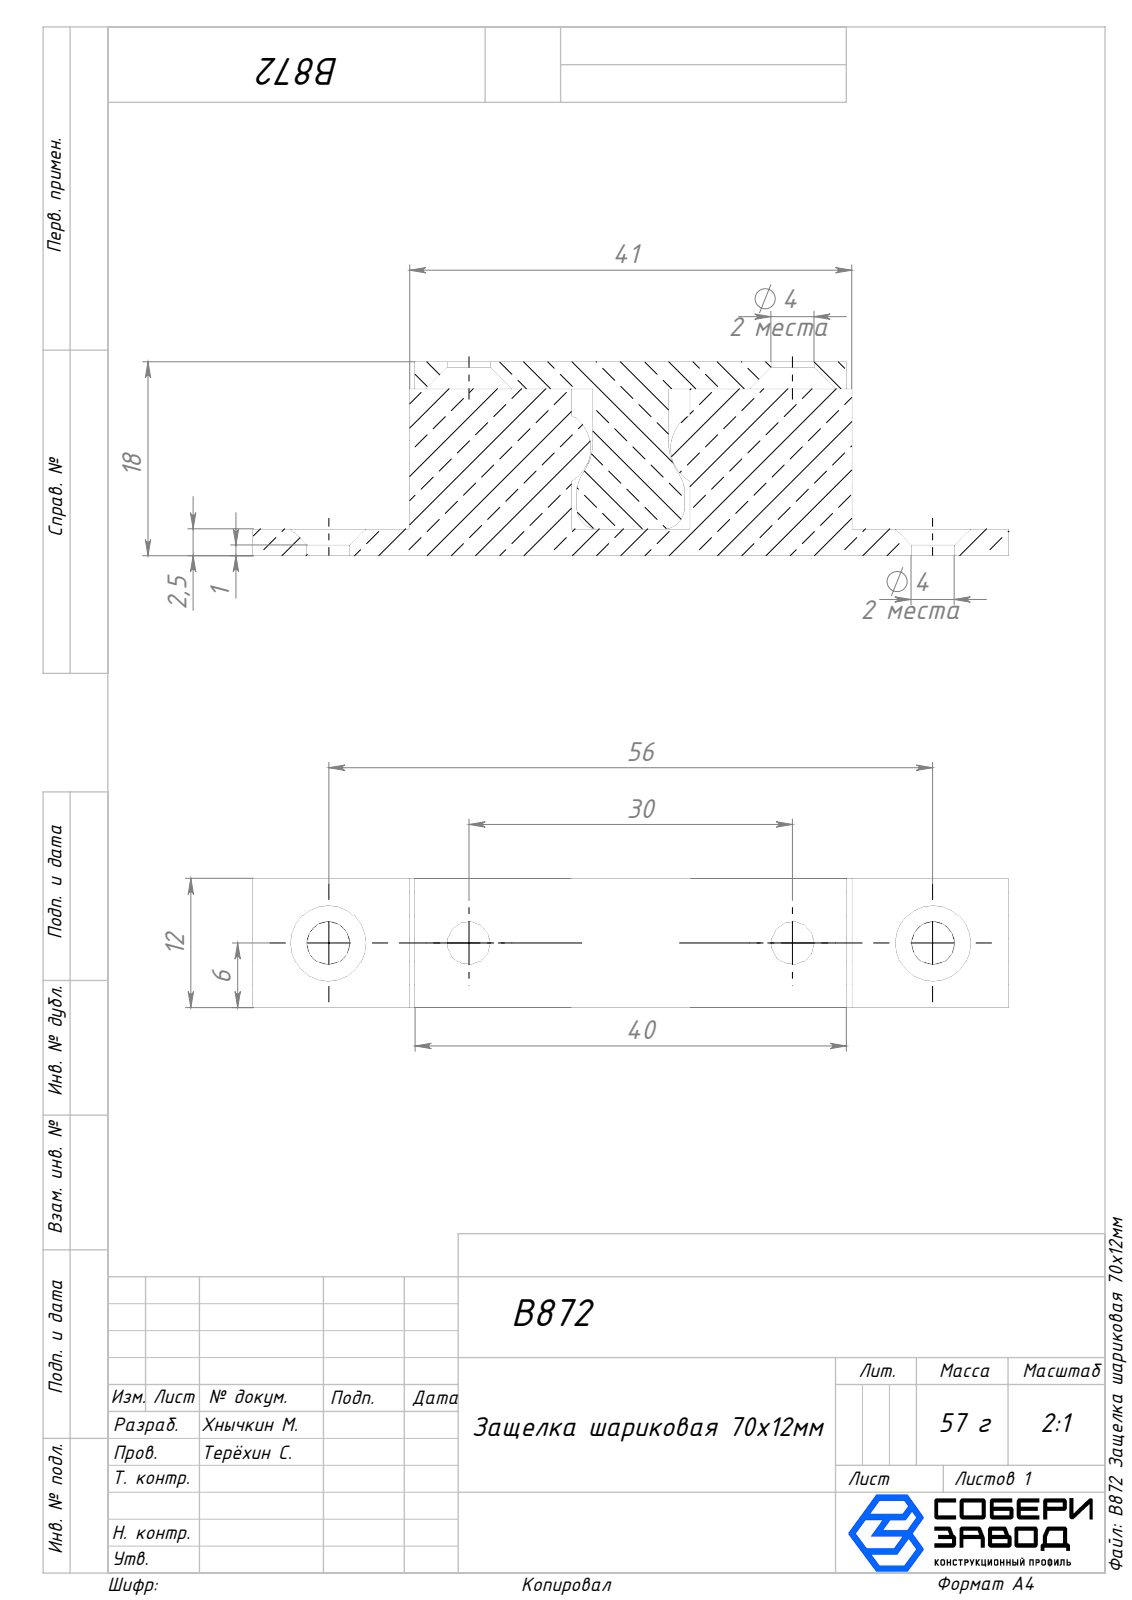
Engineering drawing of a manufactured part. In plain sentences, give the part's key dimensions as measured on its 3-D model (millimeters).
The part is named "2 часть_00; Часть_1_00; B872 Защелка шариковая 70х12мм". Its 3-D file was written by "SolidWorks 2025 (AUTOMOTIVE_DESIGN)". It is 2 solids with 50 faces: 24 planar, 16 cylindrical and 10 other. Overall it measures 70 by 18 by 12 millimeters. Its volume is 8 618 cubic millimeters and its surface area 5 055 square millimeters. Round holes: 4 of diameter 4. Partial cylindrical surfaces (rounded edges, fillets, slot ends): 2 of radius 2, 2 of radius 3.02, 2 of radius 5, 1 of radius 6. The main face-to-face distances are 15.5, 2.5, 12, 18, 15, 13, 26, 41, 14.5, 40.5. The hole center spacings are 13, 43, 30, 56.
